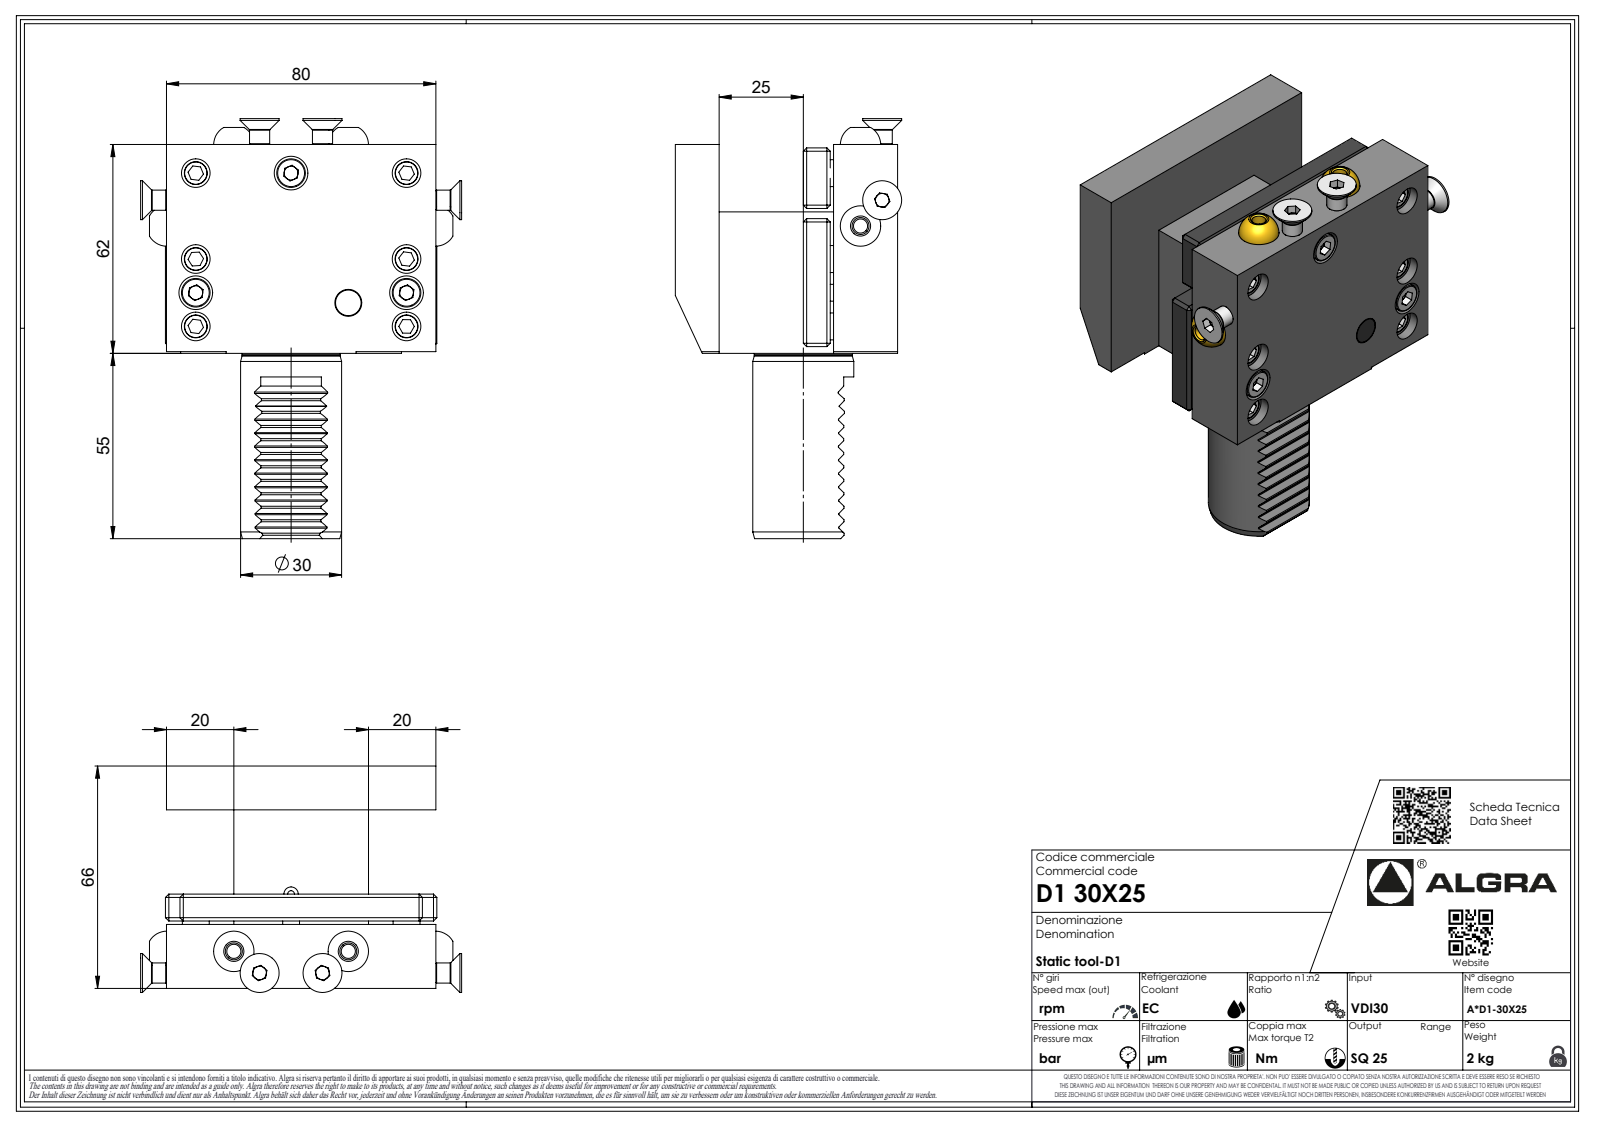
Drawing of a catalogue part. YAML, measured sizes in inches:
part_name: "D130X25"
step_written_by: "SolidWorks 2023 (AUTOMOTIVE_DESIGN)"
units: inches
bodies: {solids: 1, faces: 293, planar: 192, cylindrical: 46, other: 55}
overall_size: [4.606, 3.15, 2.598]
volume: 15.03
surface_area: 55.89
round_holes:
  - {diameter: 0.083, count: 1}
  - {diameter: 0.268, count: 1}
round_bosses_or_shafts:
  - {diameter: 1.181, count: 1}
  - {diameter: 1.146, count: 1}
  - {diameter: 0.251, count: 1}
  - {diameter: 0.067, count: 1}
partial_cylinders:
  - {radius: 0.013, count: 7}
  - {radius: 0.02, count: 7}
  - {radius: 0.146, count: 7}
  - {radius: 0.012, count: 3}
  - {radius: 0.011, count: 2}
  - {radius: 0.008, count: 1}
  - {radius: 0.009, count: 1}
  - {radius: 0.01, count: 1}
face_to_face_distances: [0.787, 2.598, 1.85, 0.748, 0.512, 1.339, 2.087, 2.362, 3.15, 2.441]
